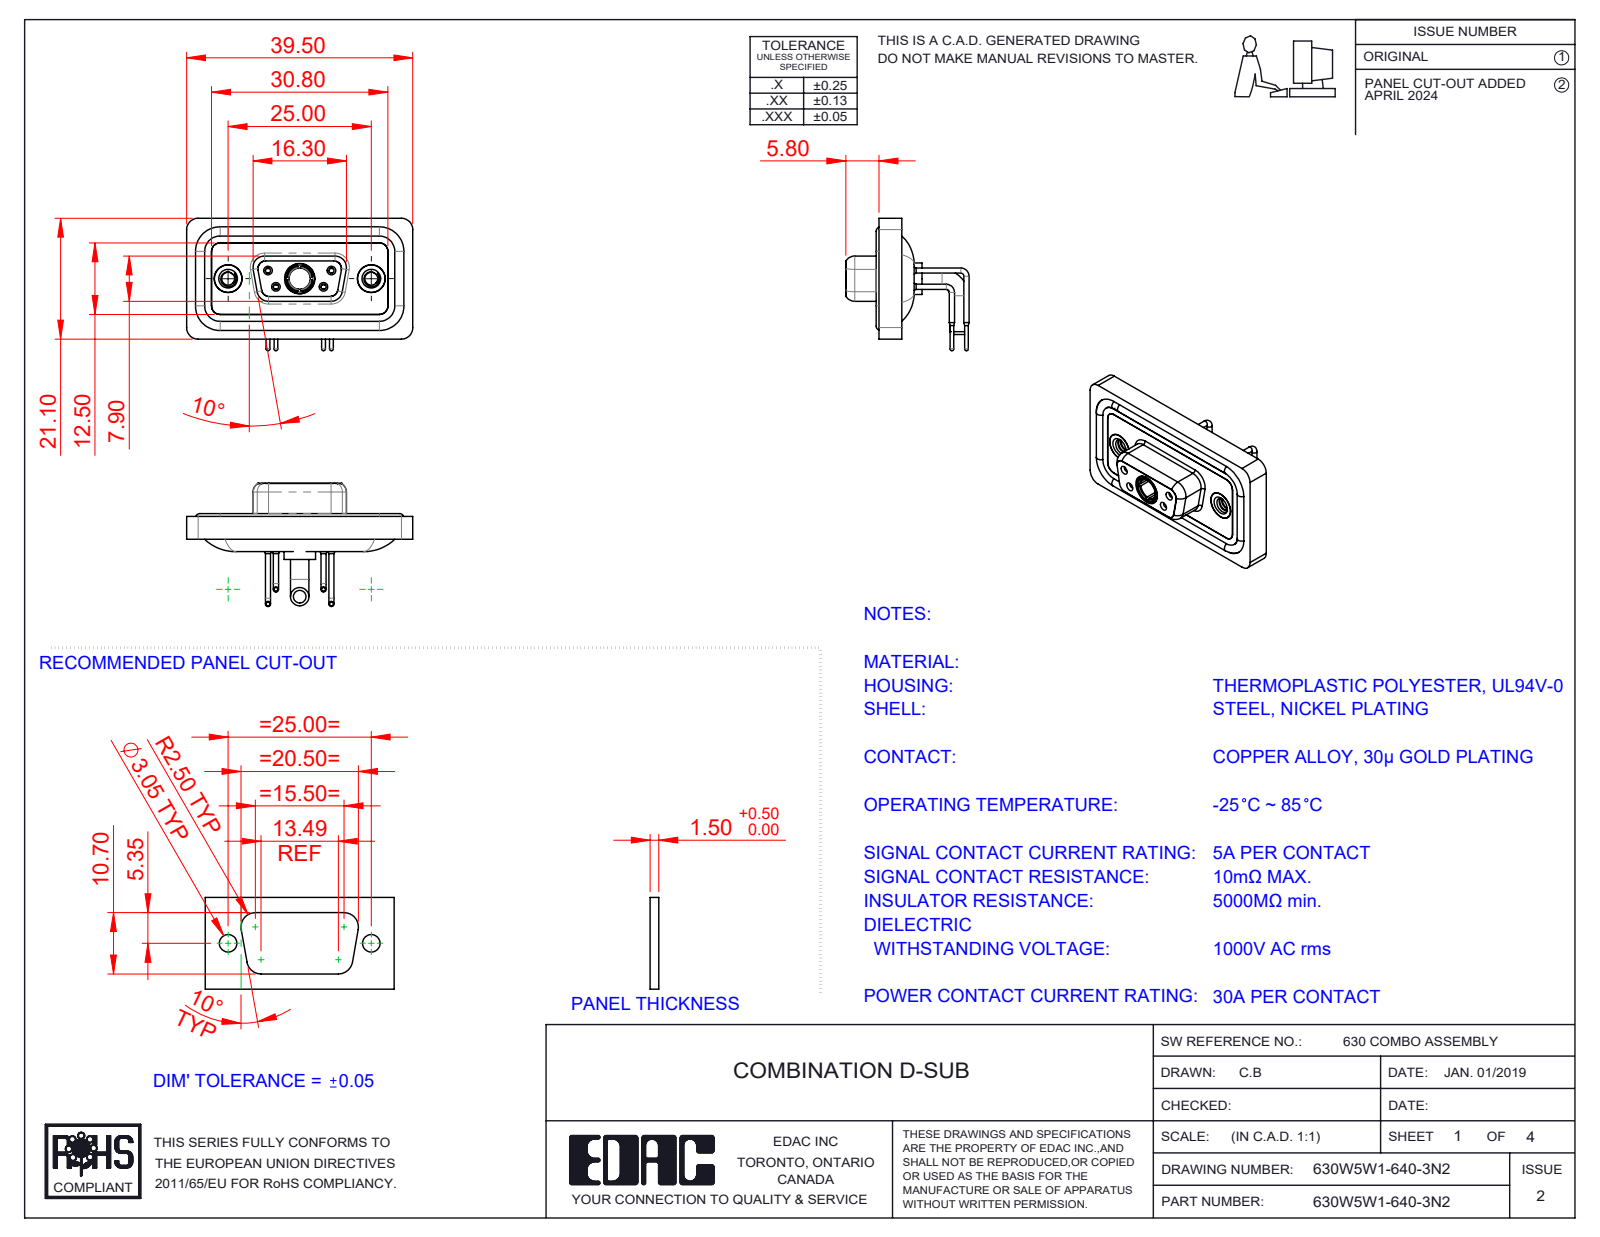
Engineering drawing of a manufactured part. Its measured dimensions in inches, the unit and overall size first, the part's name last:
Units: inches
Overall size (bounding box): 1.555 × 0.91 × 0.848
Round holes (diameter × count): ⌀0.035 ×4, ⌀0.043 ×4, ⌀0.059 ×4, ⌀0.079 ×4, ⌀0.191 ×3, ⌀0.063 ×2, ⌀0.067 ×2, ⌀0.089 ×2, ⌀0.157 ×2, ⌀0.159 ×2, ⌀0.197 ×2, ⌀0.146 ×1
Round bosses / shafts (diameter × count): ⌀0.063 ×6, ⌀0.035 ×4, ⌀0.026 ×4, ⌀0.195 ×2, ⌀0.189 ×2, ⌀0.126 ×2, ⌀0.217 ×1, ⌀0.205 ×1
Partial cylindrical surfaces — rounded edges, fillets, slot ends (radius × count): R0.059 ×18, R0.079 ×18, R0.053 ×8, R0.063 ×8, R0.01 ×4, R0.02 ×4, R0.024 ×4, R0.026 ×4
Main face-to-face distances: 0.016, 0.071, 0.043, 0.114, 0.098, 0.063, 0.122, 0.083, 0.059, 0.02
Hole centre spacings: 0.124, 0.225, 0.28, 0.492, 0.713, 0.173, 0.173, 0.327
Volume: 0.296 in³ · Surface area: 12.19 in²
Bodies: 13 solids, 676 faces (194 planar, 305 cylindrical, 177 other)
Part name (STEP PRODUCT): 630Combo Housing_5W1; 630Combo Shell Rear_09 Contacts; 630Combo Contact Row 1_50 Contacts; 630W5W1-640-3N2 (+5 more)
STEP written by: SolidWorks 2023 (CONFIG_CONTROL_DESIGN)
